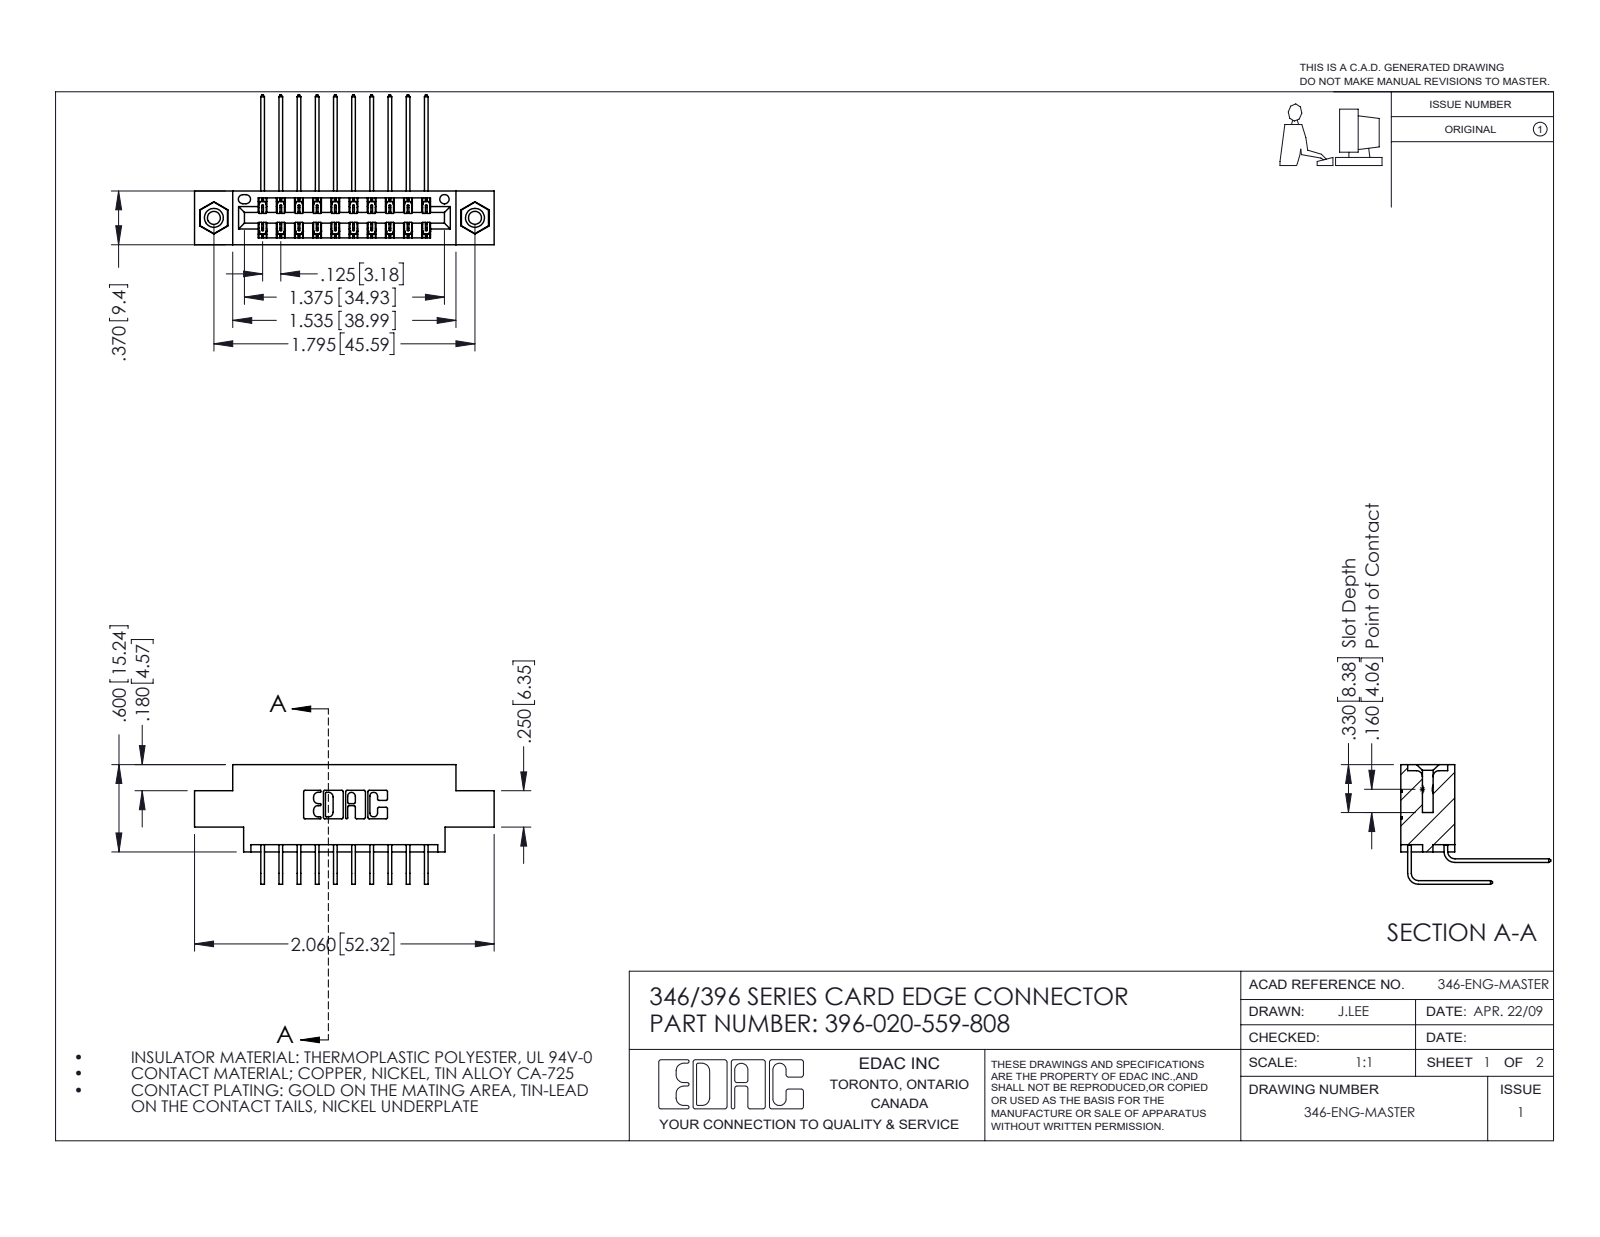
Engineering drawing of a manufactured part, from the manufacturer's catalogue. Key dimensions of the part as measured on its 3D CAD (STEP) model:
Part name (STEP PRODUCT): 345-292-001_559 Tail - 2; 345-292-001_558 559 Tail - 1; 345-250-001_345-250-003-102; 346 Part_0.170 Offset - 0.156 Dia-TI (+1 more)
STEP written by: SolidWorks 2016 (CONFIG_CONTROL_DESIGN)
Units: inches
Bodies: 23 solids, 1266 faces (852 planar, 398 cylindrical, 16 other)
Overall size (bounding box): 2.06 × 1.03 × 0.823
Volume: 0.293 in³ · Surface area: 10.63 in²
Round holes (diameter × count): ⌀0.089 ×2, ⌀0.125 ×2, ⌀0.156 ×2, ⌀0.064 ×1
Round bosses / shafts (diameter × count): ⌀0.155 ×2
Partial cylindrical surfaces — rounded edges, fillets, slot ends (radius × count): R0.006 ×30, R0.01 ×22, R0.007 ×6, R0.031 ×6, R0.026 ×3, R0.014 ×2, R0.022 ×2, R0.024 ×2
Main face-to-face distances: 0.25, 0.048, 0.322, 0.37, 0.025, 0.072, 0.298, 0.222, 0.148, 0.275
Hole centre spacings: 0.246, 1.59, 1.795
